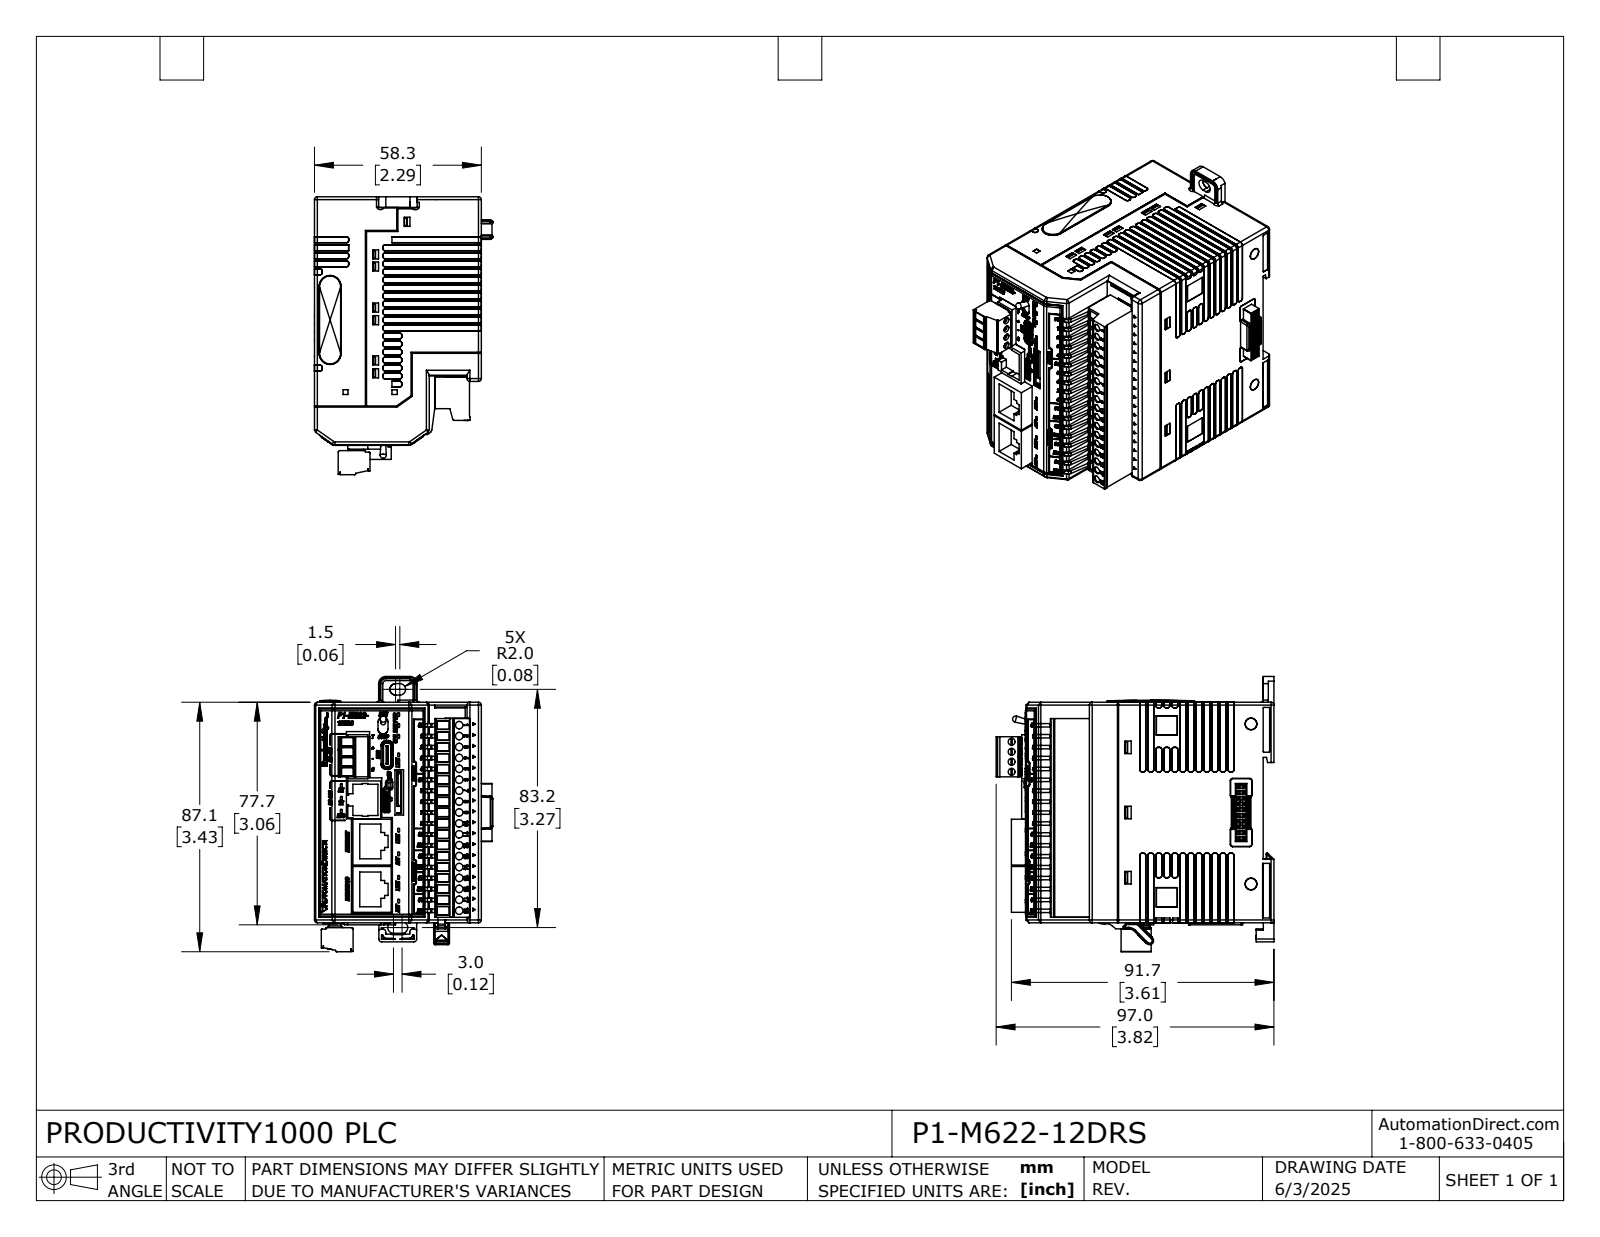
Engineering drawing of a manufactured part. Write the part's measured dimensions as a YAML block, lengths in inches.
part_name: "P1-M622-12DRS"
step_written_by: "SolidWorks 2024 (AUTOMOTIVE_DESIGN)"
units: inches
bodies: {solids: 12, faces: 3707, planar: 2117, cylindrical: 886, other: 704}
overall_size: [3.686, 3.61, 2.452]
volume: 2.158
surface_area: 118.3
partial_cylinders:
  - {radius: 0.01, count: 186}
  - {radius: 0.008, count: 80}
  - {radius: 0.02, count: 53}
  - {radius: 0.039, count: 33}
  - {radius: 0.079, count: 8}
  - {radius: 0.024, count: 7}
  - {radius: 0.059, count: 7}
  - {radius: 0.012, count: 4}
face_to_face_distances: [0.05, 0.02, 2.235, 0.039, 2.275, 3.01, 3.022, 2.294, 3.02, 3.031]
